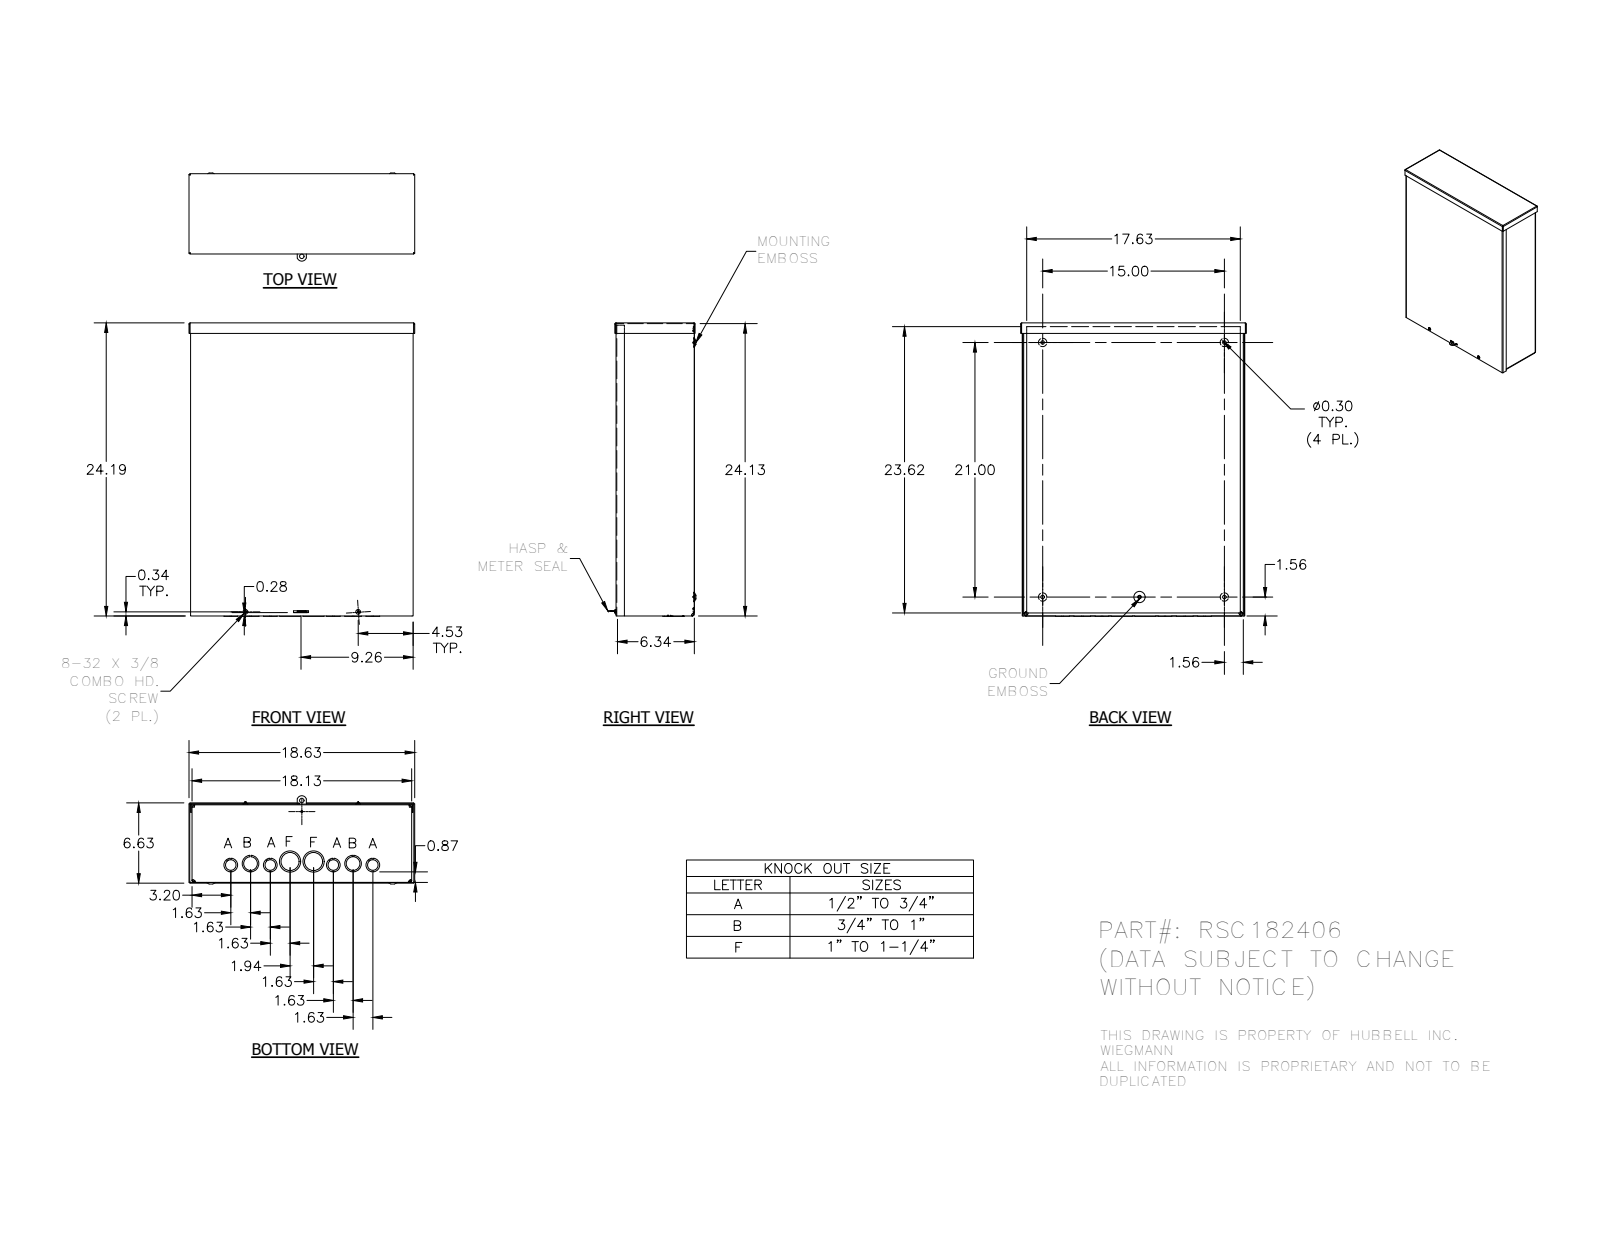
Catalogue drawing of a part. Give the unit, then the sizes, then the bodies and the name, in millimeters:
Units: millimetres
Overall size (bounding box): 616.7 × 473.1 × 181
Round holes (diameter × count): ⌀28.6 ×6, ⌀7.6 ×4, ⌀8 ×4, ⌀22.2 ×4, ⌀3.2 ×2, ⌀3.8 ×2, ⌀34.9 ×2, ⌀38.1 ×2, ⌀44.5 ×2, ⌀4 ×1, ⌀4.2 ×1, ⌀9.5 ×1
Round bosses / shafts (diameter × count): ⌀9.8 ×2, ⌀4.2 ×2, ⌀5.8 ×1
Partial cylindrical surfaces — rounded edges, fillets, slot ends (radius × count): R0.3 ×15, R0.8 ×8, R2.4 ×8, R3.2 ×8, R4.7 ×8, R0.8 ×6, R0.6 ×5, R1.4 ×4
Main face-to-face distances: 1.6, 158.7, 157.1, 1.6, 160.3, 158.8, 1.6, 460.4, 612.8, 3.1
Hole centre spacings: 41.5, 214.9, 42.1, 82.8, 82.9, 91, 124.4, 126.2
Volume: 1 722 000 mm³ · Surface area: 2 204 000 mm²
Bodies: 7 solids, 619 faces (304 planar, 171 cylindrical, 144 other)
Part name (STEP PRODUCT): RSC182406; RSC182406_WRAP; RSC1824_LID; RSC1806_CAP (+4 more)
STEP written by: Autodesk Inventor 2012 (AUTOMOTIVE_DESIGN)
